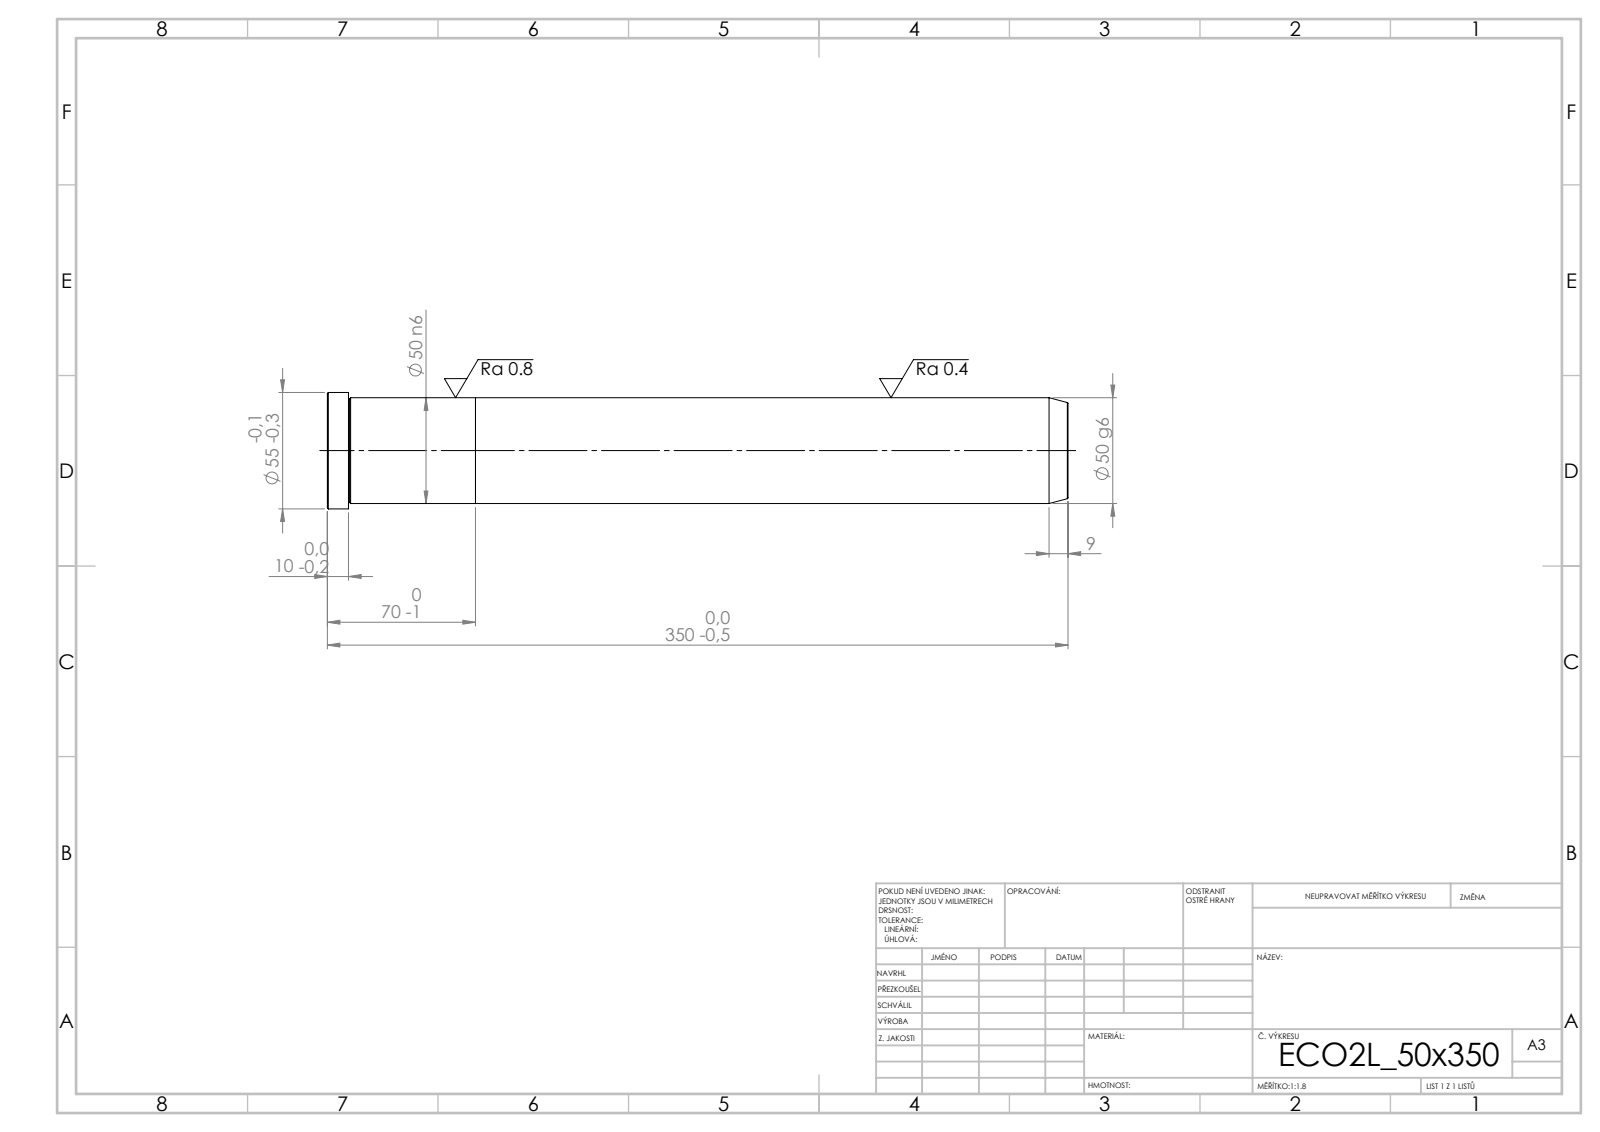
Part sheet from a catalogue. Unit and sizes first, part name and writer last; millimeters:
Units: millimetres
Overall size (bounding box): 350 × 55 × 55
Round bosses / shafts (diameter × count): ⌀55 ×1, ⌀50 ×1
Main face-to-face distances: 70, 280, 350, 340, 60, 10
Volume: 689 610 mm³ · Surface area: 63 452 mm²
Bodies: 2 solids, 21 faces (5 planar, 6 cylindrical, 10 other)
STEP written by: SolidWorks 2019 (CONFIG_CONTROL_DESIGN)
